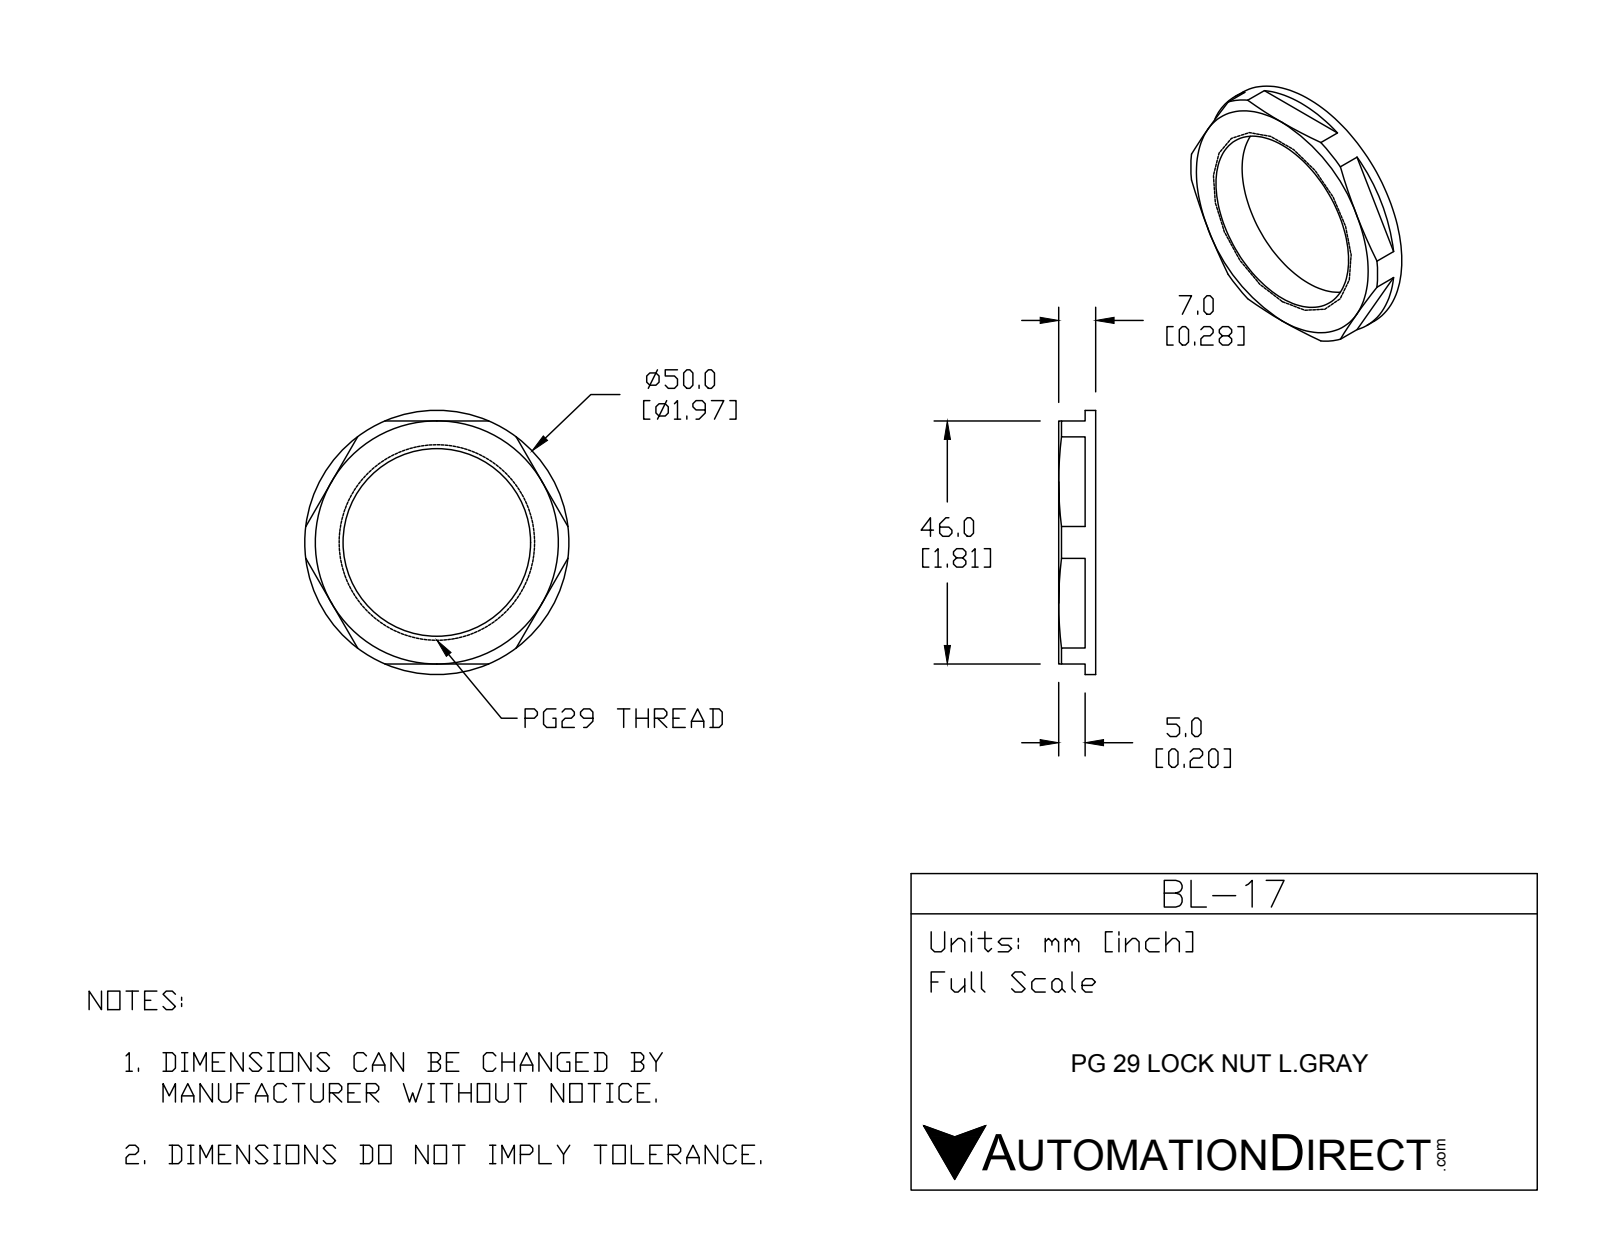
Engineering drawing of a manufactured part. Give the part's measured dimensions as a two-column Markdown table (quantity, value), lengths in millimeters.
| quantity | value |
| --- | --- |
| part name | BL-17 |
| STEP written by | SolidWorks 2015 (CONFIG_CONTROL_DESIGN) |
| units | millimeters |
| bodies | 1 solid, 33 faces (17 planar, 10 cylindrical, 6 other) |
| overall size | 50 × 50 × 7 |
| volume | 5 993 mm³ |
| surface area | 3 780 mm² |
| round holes (diameter × count) | 1.5 × 3, 35.5 × 1 |
| round bosses / shafts (diameter × count) | 50 × 1 |
| main face-to-face distances | 7, 46, 2, 5, 1.7, 6.7 |
| hole center spacings | 23.55, 40.78, 23.54, 40.79 |
